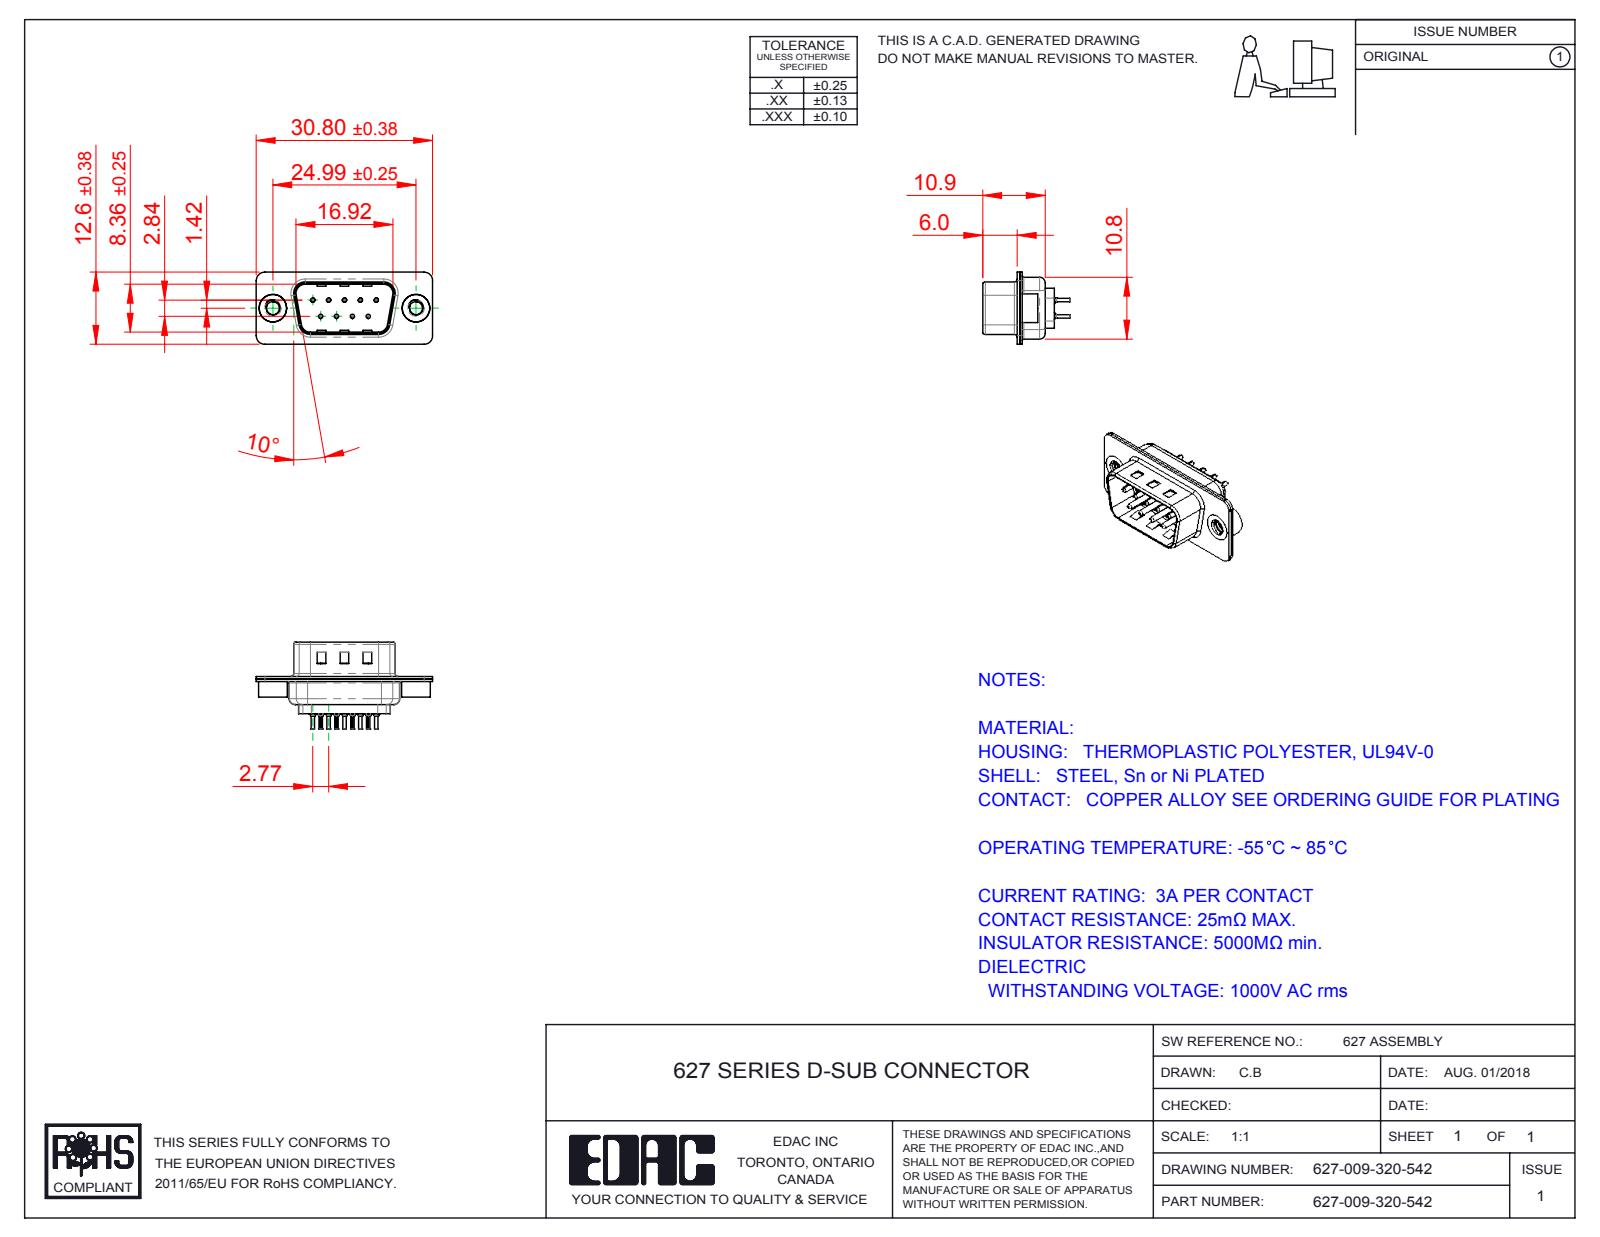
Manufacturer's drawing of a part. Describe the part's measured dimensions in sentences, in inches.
The part is named "627 Contact Row 2_20L; 627 Housing_09 LP; 627 Contact Row 1_20L; 627 Shell Rear_09 Contacts (+3 more)". Its 3-D file was written by "SolidWorks 2016 (CONFIG_CONTROL_DESIGN)". It is 14 solids with 1186 faces: 323 planar, 462 cylindrical and 401 other. Overall it measures 1.213 by 0.598 by 0.496 inches. Its volume is 0.08 cubic inches and its surface area 6.023 square inches. Round holes: 9 of diameter 0.008, 9 of diameter 0.014, 9 of diameter 0.043, 9 of diameter 0.063, 2 of diameter 0.089, 2 of diameter 0.157, 2 of diameter 0.189. Round bosses or shafts: 9 of diameter 0.079, 9 of diameter 0.059, 9 of diameter 0.03, 9 of diameter 0.024, 2 of diameter 0.197, 2 of diameter 0.193. Partial cylindrical surfaces (rounded edges, fillets, slot ends): 18 of radius 0.004, 18 of radius 0.059, 12 of radius 0.079, 8 of radius 0.02, 8 of radius 0.063, 4 of radius 0.01, 4 of radius 0.024, 4 of radius 0.026. The main face-to-face distances are 0.018, 0.016, 0.035, 0.032, 0.377, 0.055, 0.345, 0.02, 0.059, 0.22. The hole center spacings are 0.124, 0.109, 0.218, 0.198, 0.198, 0.327, 0.294, 0.295.
